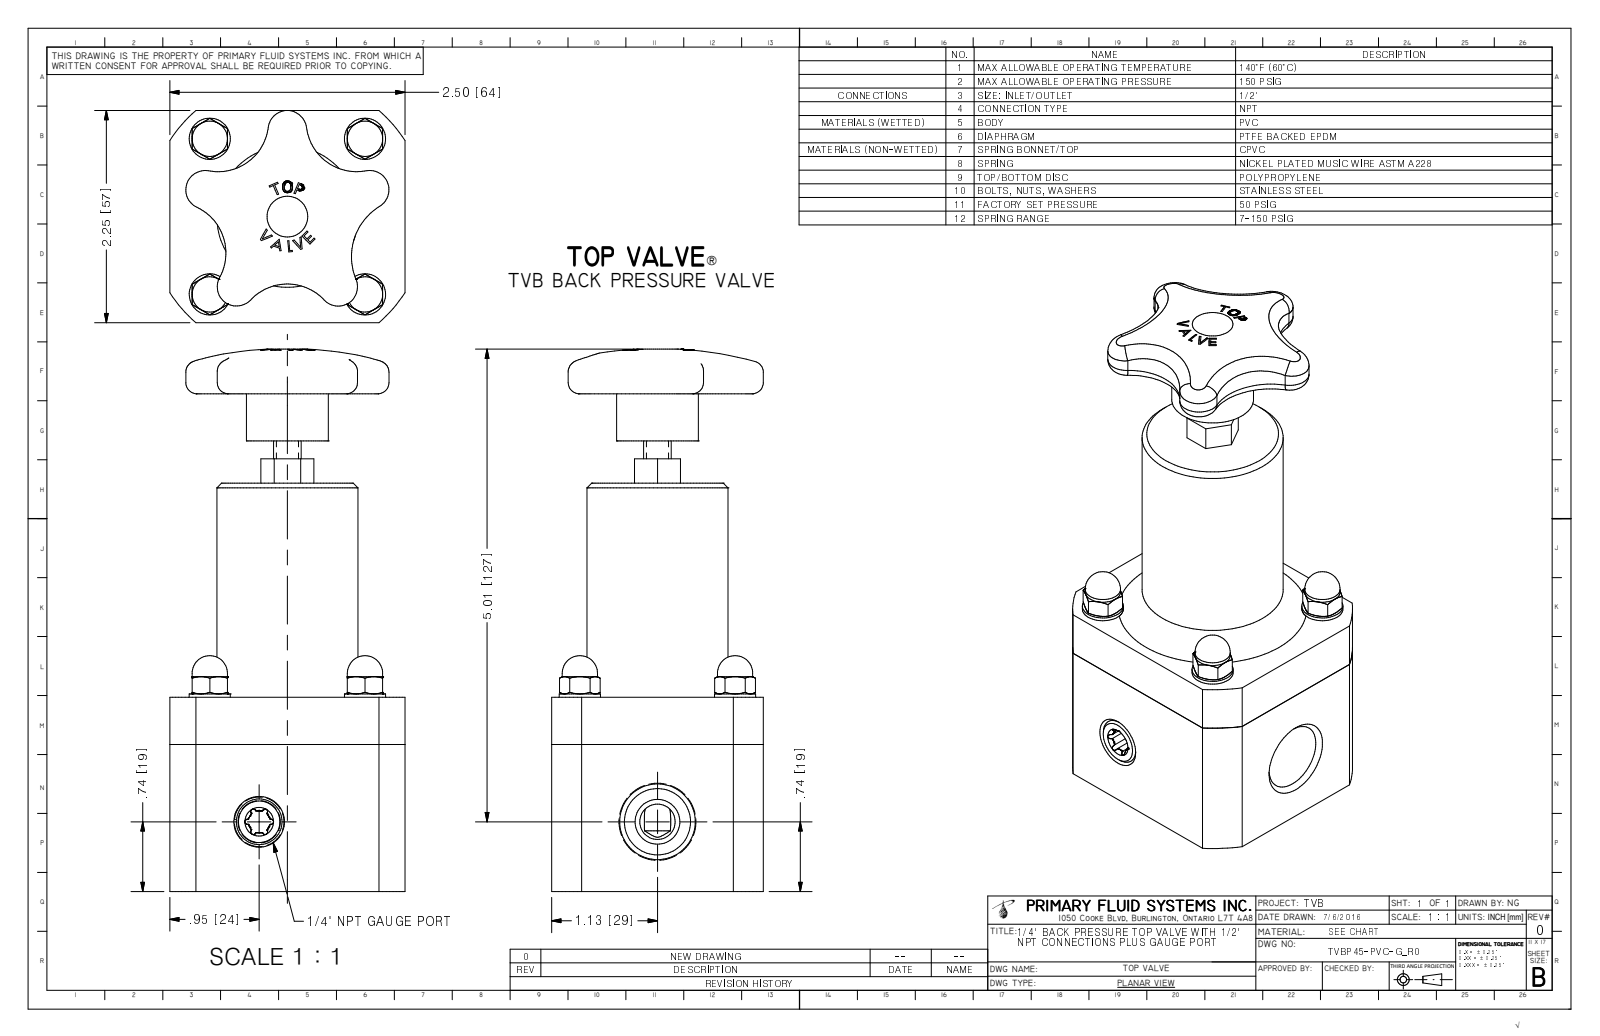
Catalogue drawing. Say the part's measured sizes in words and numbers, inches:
The part is named "TVBP45-PVC-G_R0". Its 3-D file was written by "Autodesk Inventor 2009 (AUTOMOTIVE_DESIGN)". It is 1 solid with 359 faces: 148 planar, 51 cylindrical and 160 other. Overall it measures 5.752 by 2.5 by 2.25 inches. Its volume is 16.17 cubic inches and its surface area 56.42 square inches. Round holes: 4 of diameter 0.147, 1 of diameter 0.703, 1 of diameter 0.719. Round bosses or shafts: 4 of diameter 0.437, 4 of diameter 0.375, 4 of diameter 0.312, 1 of diameter 1.5, 1 of diameter 0.87, 1 of diameter 0.293. Partial cylindrical surfaces (rounded edges, fillets, slot ends): 6 of radius 0.027, 5 of radius 0.085, 5 of radius 0.205, 4 of radius 0.536, 4 of radius 0.656, 1 of radius 0.625, 1 of radius 0.745, 1 of radius 1.488. The main face-to-face distances are 2.25, 2.5, 2.06, 4.33, 2.27, 0.6, 1.9, 4.778, 2.718, 0.448. The hole center spacings are 1.65, 1.65, 2.333, 2.334.
